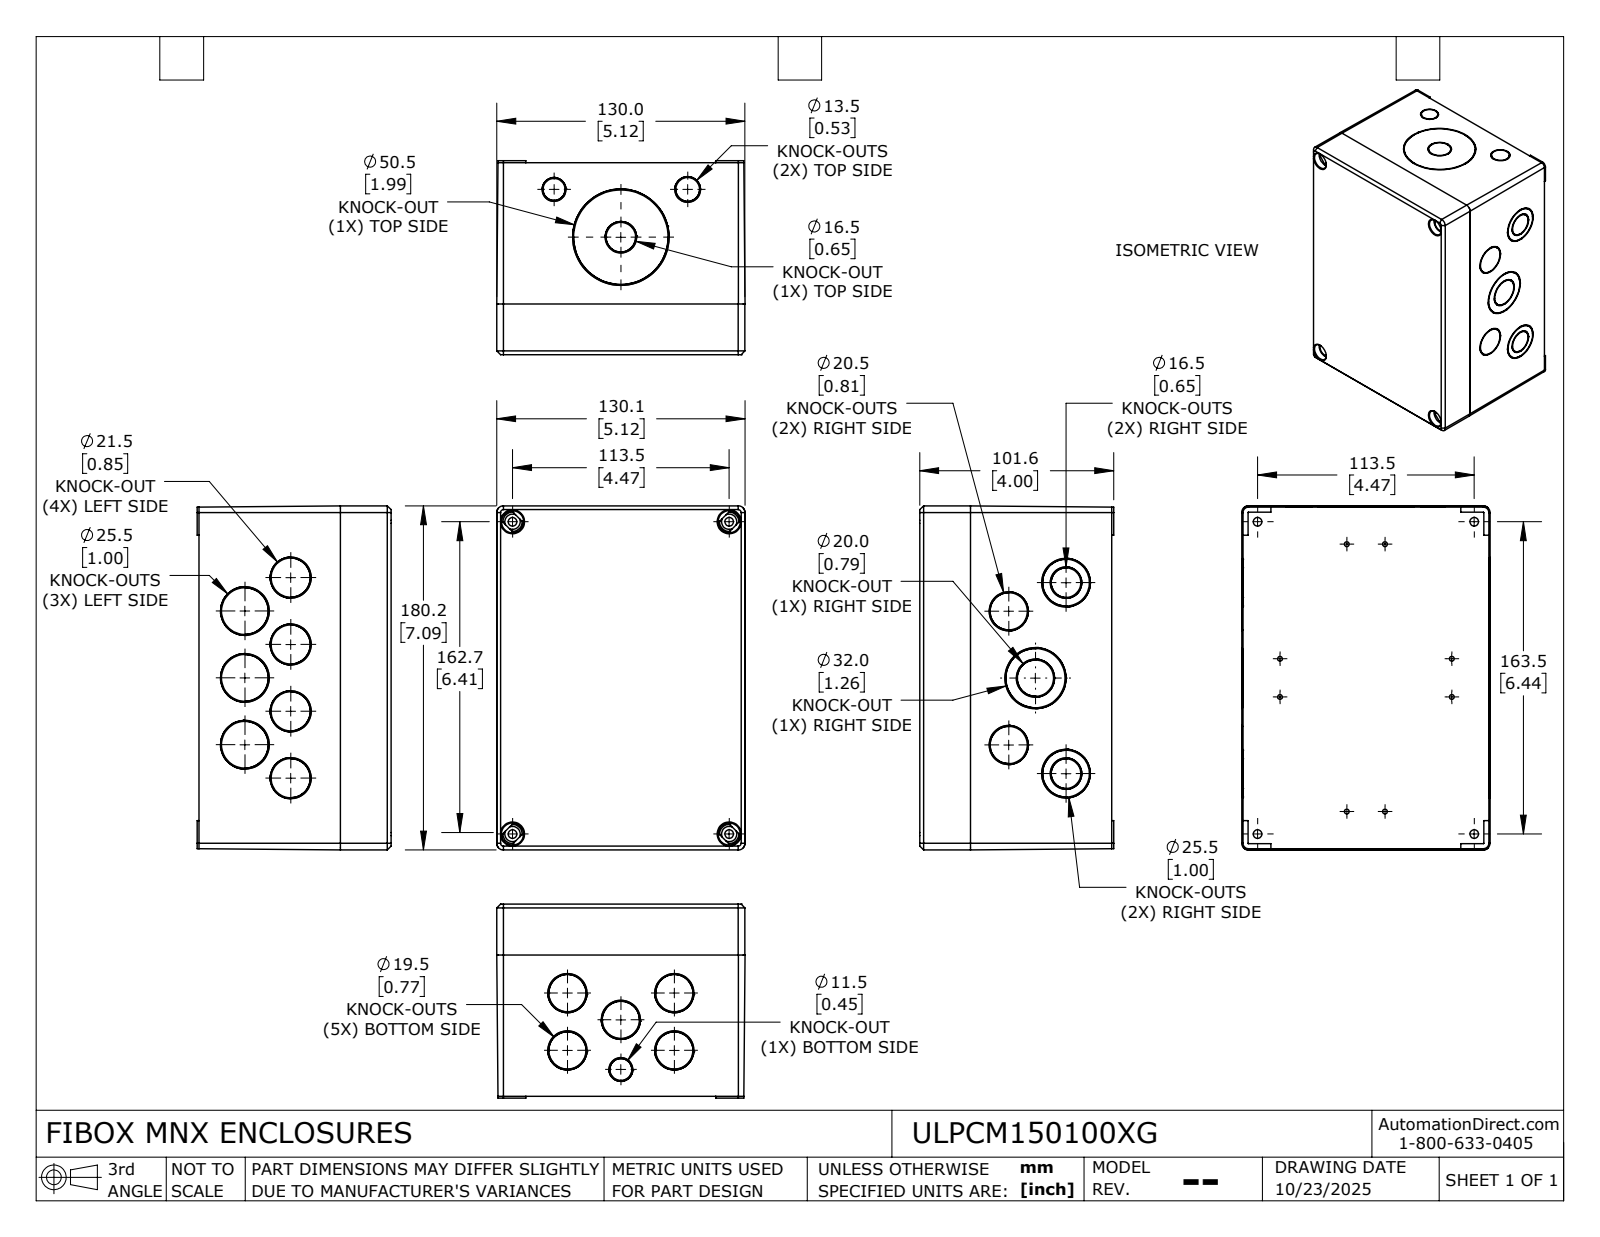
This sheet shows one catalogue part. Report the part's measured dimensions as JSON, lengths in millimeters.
{"part_name": "ULPCM150100XG", "step_written_by": "SolidWorks 2024 (AUTOMOTIVE_DESIGN)", "units": "millimeters", "bodies": {"solids": 2, "faces": 906, "planar": 706, "cylindrical": 164, "other": 36}, "overall_size": [180.2, 130.09, 101.6], "volume_mm3": 585312, "surface_area_mm2": 218840, "round_holes": [[2.5, 8], [3.2, 8], [25.5, 5], [4.5, 4], [8, 4], [11.6, 4], [20.5, 4], [21.5, 4], [16.5, 3], [12.5, 2], [13.5, 1], [20, 1]], "round_bosses_or_shafts": [[8, 8], [19.5, 7], [24.5, 5], [20.5, 4], [15.5, 3], [11.5, 2], [49.5, 1], [31, 1]], "partial_cylinders_radius": [[3.3, 8], [10.25, 6], [0.2, 4], [2.6, 4], [2.7, 4], [2.85, 4], [3.5, 4], [5.03, 4]], "face_to_face_distances": [4.22, 100.6, 4.2, 96.4, 97.9, 93.7, 2.7, 26.6, 74, 69.8], "hole_center_spacings": [10, 29.7, 35, 70, 90, 20, 33.85, 40]}
